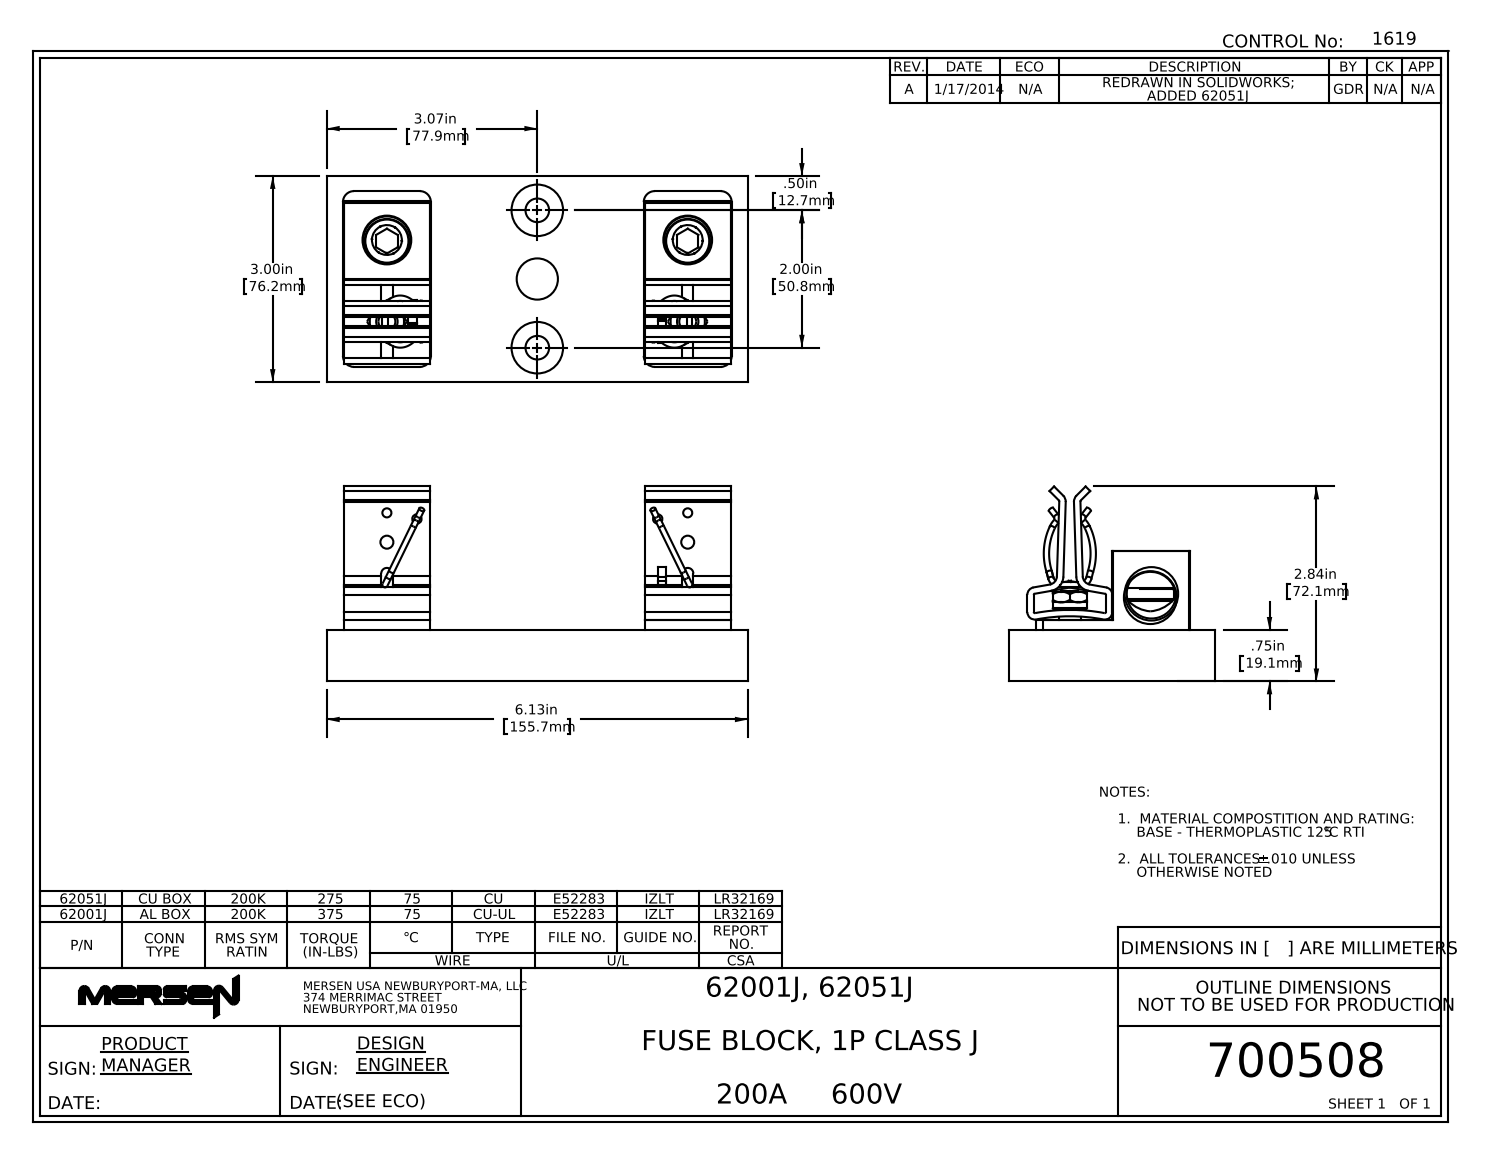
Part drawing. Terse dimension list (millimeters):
name: 700508revA
written by: SolidWorks 2013 (AUTOMOTIVE_DESIGN)
unit: mm
bodies: 19 solids, 647 faces (370 planar, 148 cylindrical, 129 other)
size: 155.7 × 76.2 × 72.1
volume: 227 800 mm³; area: 125 700 mm²
holes: 3× ⌀19.1, 2× ⌀3.4, 2× ⌀3.5, 2× ⌀4.8, 2× ⌀8, 2× ⌀8.6, 2× ⌀8.7, 2× ⌀8.7, 2× ⌀9.6, 2× ⌀17.4, 2× ⌀21.6, 1× ⌀15.9
bosses: 8× ⌀2, 2× ⌀26.7, 2× ⌀19.1, 2× ⌀17.5, 2× ⌀15.1, 2× ⌀12.7
rounds: 8× R4.1, 4× R0.4, 4× R1.7, 4× R2.8, 4× R3.2, 4× R7.2, 2× R0.8, 2× R2.1
face distances: 3.2, 3.2, 2.5, 31.8, 6.4, 34.9, 2.4, 111.3, 48.4, 104.1
hole spacings: 111.3, 0.4, 10.8, 11.3, 14, 29.8, 30.2, 56.5
